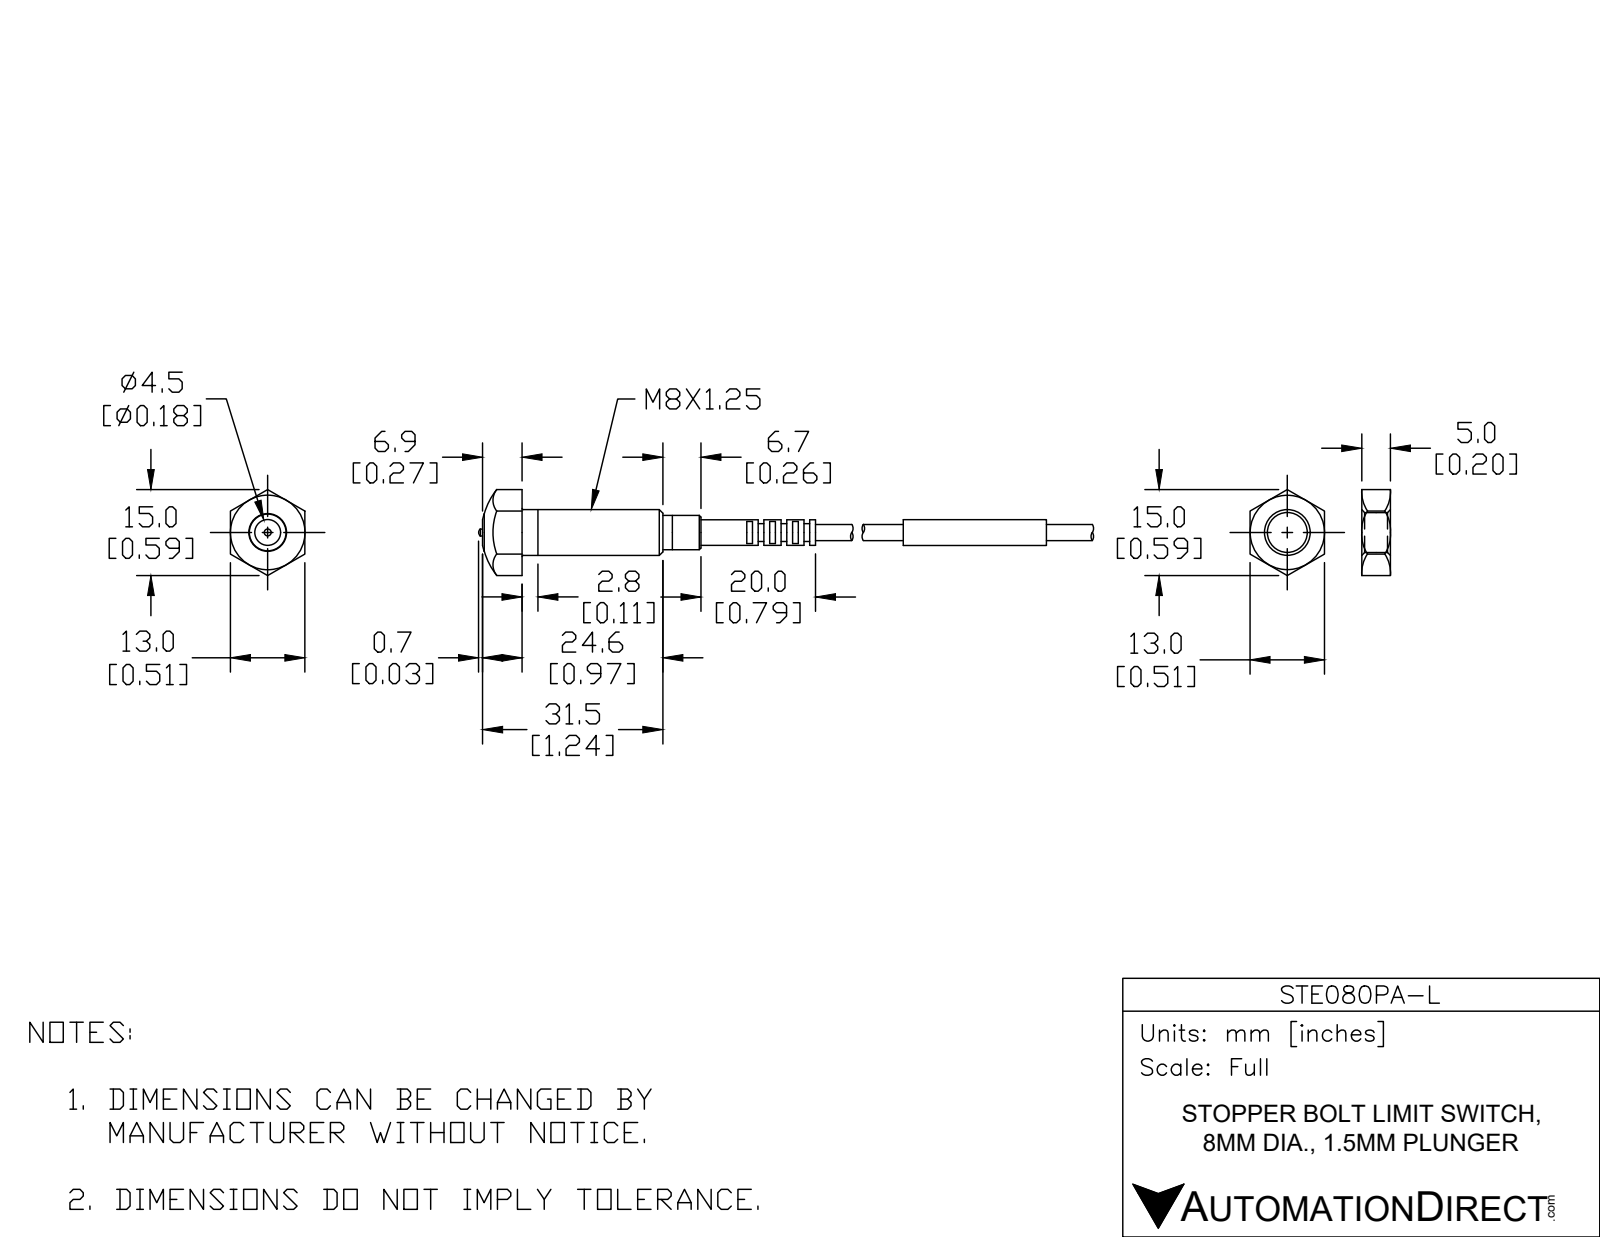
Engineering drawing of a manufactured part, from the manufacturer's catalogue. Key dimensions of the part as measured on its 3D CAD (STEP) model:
Part name (STEP PRODUCT): STE080PA-L
STEP written by: SolidWorks 2017 (CONFIG_CONTROL_DESIGN)
Units: millimetres
Bodies: 2 solids, 166 faces (66 planar, 74 cylindrical, 26 other)
Overall size (bounding box): 107.84 × 15.01 × 13
Volume: 2 900 mm³ · Surface area: 2 493 mm²
Round bosses / shafts (diameter × count): ⌀8 ×1, ⌀6.4 ×1, ⌀6 ×1, ⌀4.5 ×1, ⌀4.45 ×1, ⌀3.1 ×1, ⌀2.8 ×1, ⌀1.2 ×1
Main face-to-face distances: 13, 1, 2, 3, 4, 6, 5, 7, 8, 9
